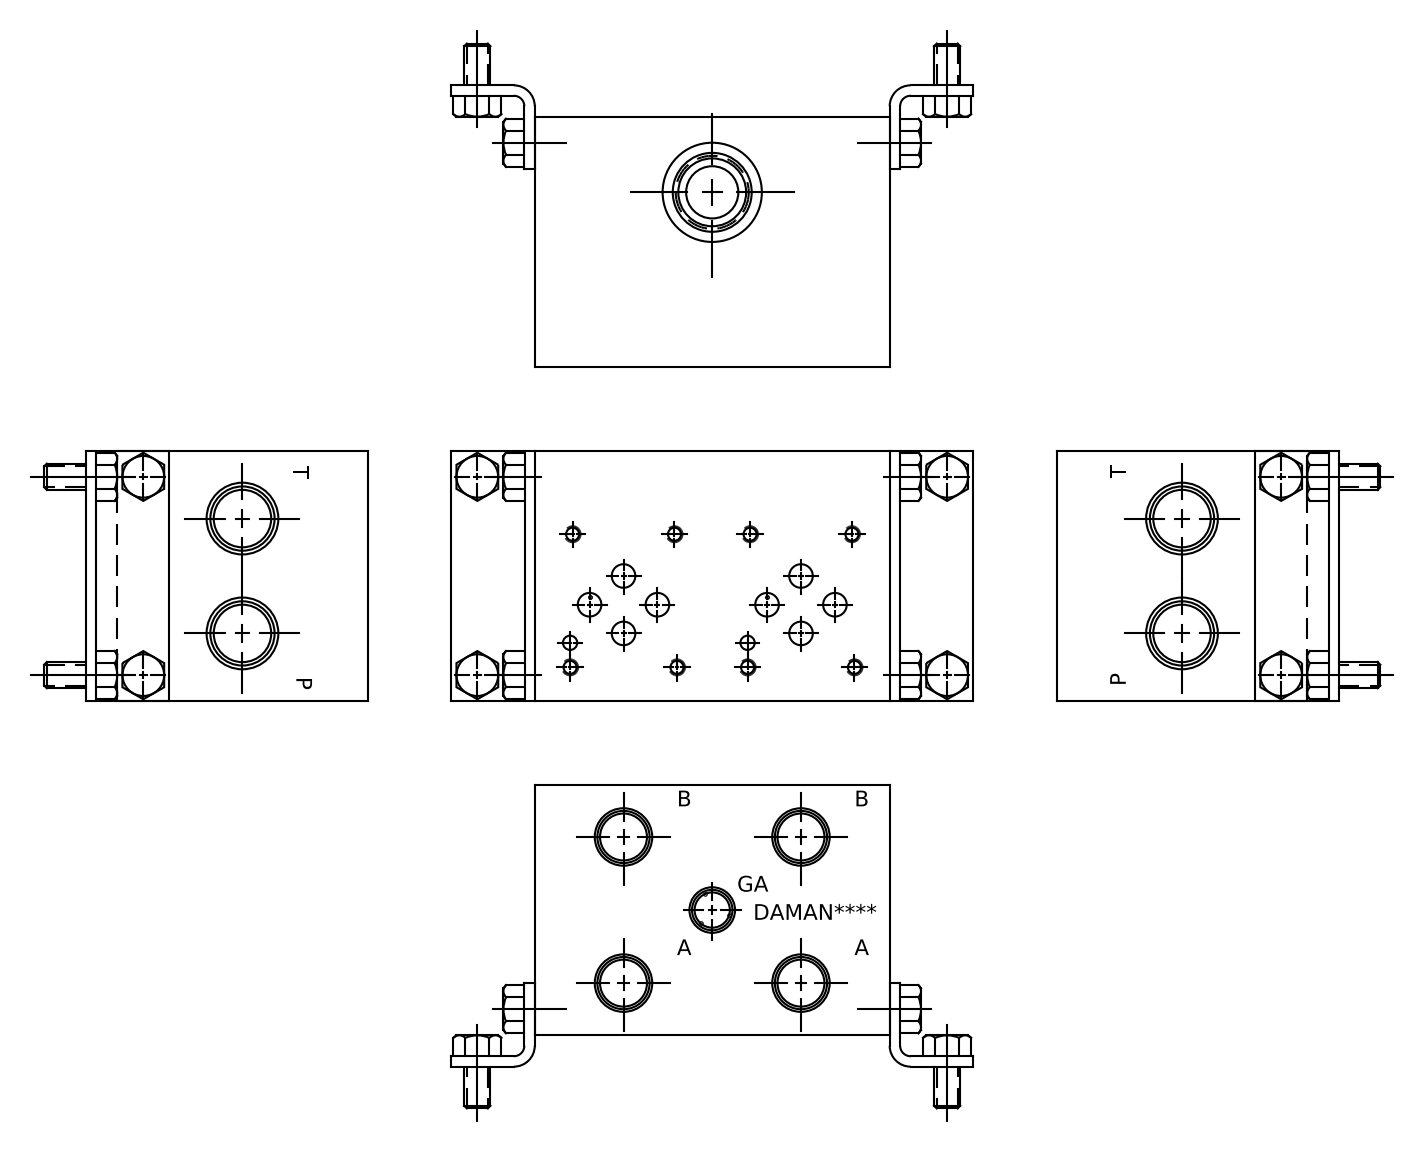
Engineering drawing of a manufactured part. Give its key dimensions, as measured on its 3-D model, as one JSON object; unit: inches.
{"part_name": "Part_AD03P022P_C_3D", "step_written_by": "Autodesk Inventor 2021 (AUTOMOTIVE_DESIGN)", "units": "inches", "bodies": {"solids": 1, "faces": 632, "planar": 359, "cylindrical": 62, "other": 211}, "overall_size": [4.25, 3, 3], "volume_in3": 33.88, "surface_area_in2": 96.39, "round_holes": [[0.149, 8], [0.19, 8], [0.281, 6], [0.563, 5], [0.681, 4], [0.156, 2], [0.25, 2], [0.257, 2], [0.312, 2], [0.625, 2], [0.688, 2], [0.85, 2]], "face_to_face_distances": [3, 4.25, 0.605, 3.645, 0.462, 2.538, 0.031, 2.969, 2.507, 3.04], "hole_center_spacings": [2.125, 0.785, 0.868, 1.321, 1.594, 2.026, 2.125, 0.295]}
